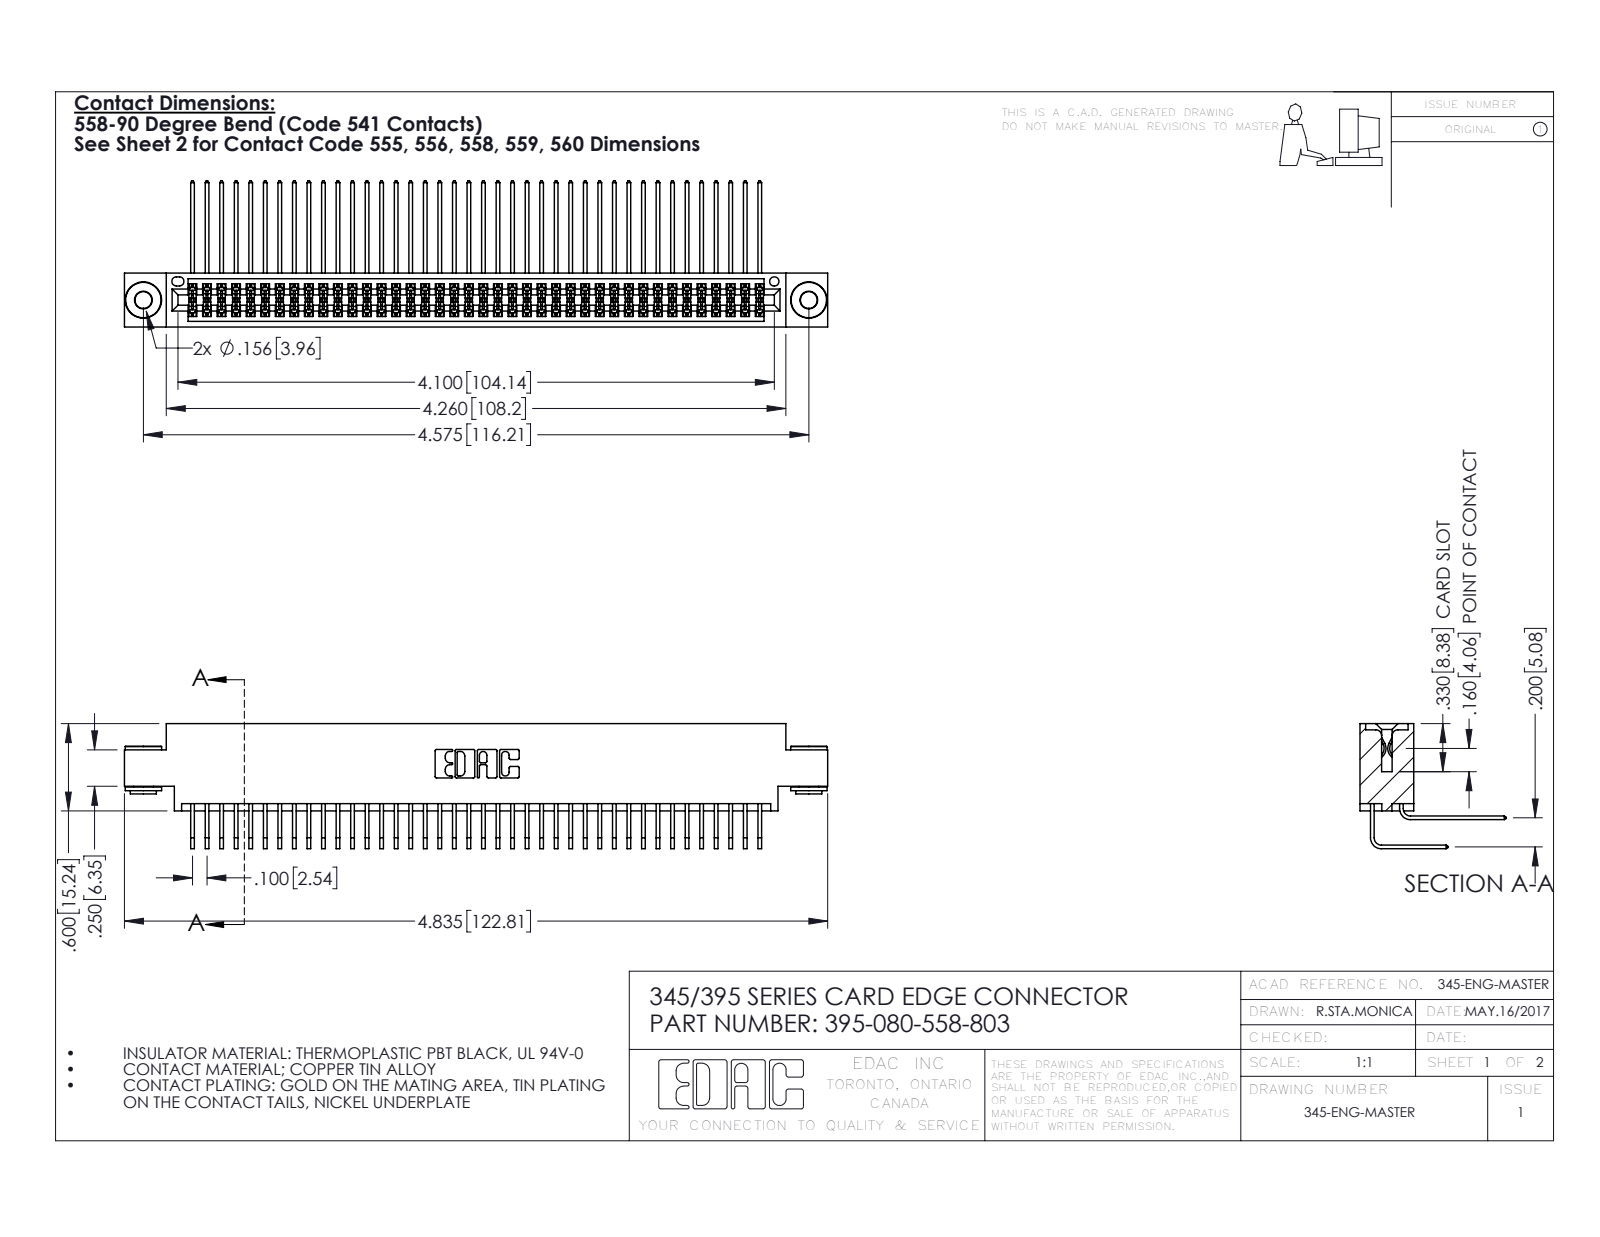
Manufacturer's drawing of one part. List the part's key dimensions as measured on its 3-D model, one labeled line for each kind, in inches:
Part name (STEP PRODUCT): 345 Part_0.170 Offset - 0.156 Dia-TH; 345-292-001_558 Tail - 2; 345-292-001_558 559 Tail - 1; 345-250-002_345-250-002-102 (+1 more)
STEP written by: SolidWorks 2016 (CONFIG_CONTROL_DESIGN)
Units: inches
Bodies: 83 solids, 4328 faces (2894 planar, 1426 cylindrical, 8 other)
Overall size (bounding box): 4.835 × 1.005 × 0.859
Volume: 0.749 in³ · Surface area: 31.98 in²
Round holes (diameter × count): ⌀0.116 ×2, ⌀0.156 ×2, ⌀0.064 ×1
Round bosses / shafts (diameter × count): ⌀0.25 ×2, ⌀0.18 ×2, ⌀0.136 ×2
Partial cylindrical surfaces — rounded edges, fillets, slot ends (radius × count): R0.006 ×121, R0.01 ×22, R0.007 ×6, R0.031 ×6, R0.026 ×3, R0.014 ×2, R0.019 ×2, R0.022 ×2
Main face-to-face distances: 0.072, 0.298, 0.2, 0.37, 0.098, 0.272, 0.025, 0.225, 0.175, 0.025
Hole centre spacings: 0.27, 4.339, 4.575
